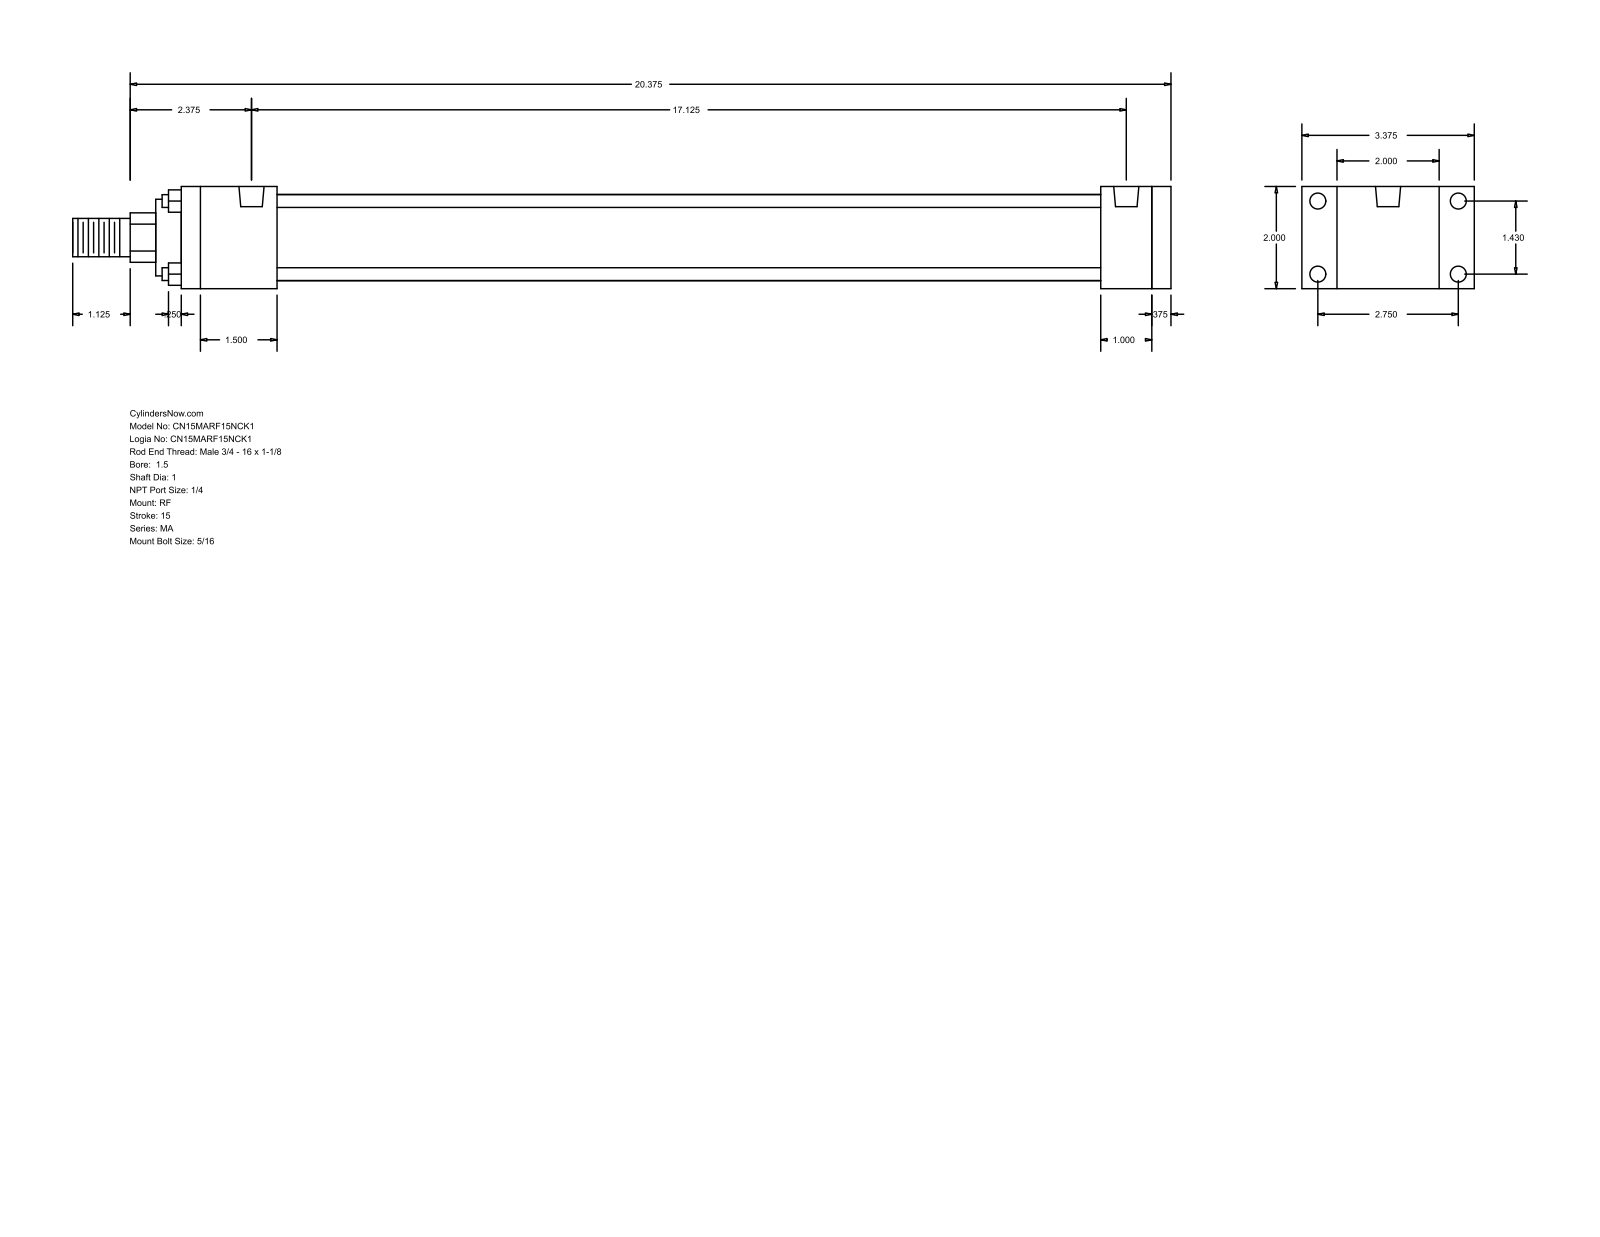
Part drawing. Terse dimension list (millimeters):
name: MA_RF__0150_1
written by: GSSL Pune (CONFIG_CONTROL_DESIGN)
unit: mm
bodies: 0 solids, 92 faces (64 planar, 28 cylindrical, 0 other)
size: 546.1 × 85.72 × 50.8
holes: 8× ⌀7.94, 2× ⌀12.49
bosses: 4× ⌀6.35, 1× ⌀42.93, 1× ⌀38.1, 1× ⌀25.4, 1× ⌀19.05
rounds: 1× R12.29
face distances: 50.8, 9.52, 492.12, 482.6, 25.4, 457.2, 34.92, 47.63, 409.57, 434.97
hole spacings: 36.32, 69.84, 78.72, 434.97
